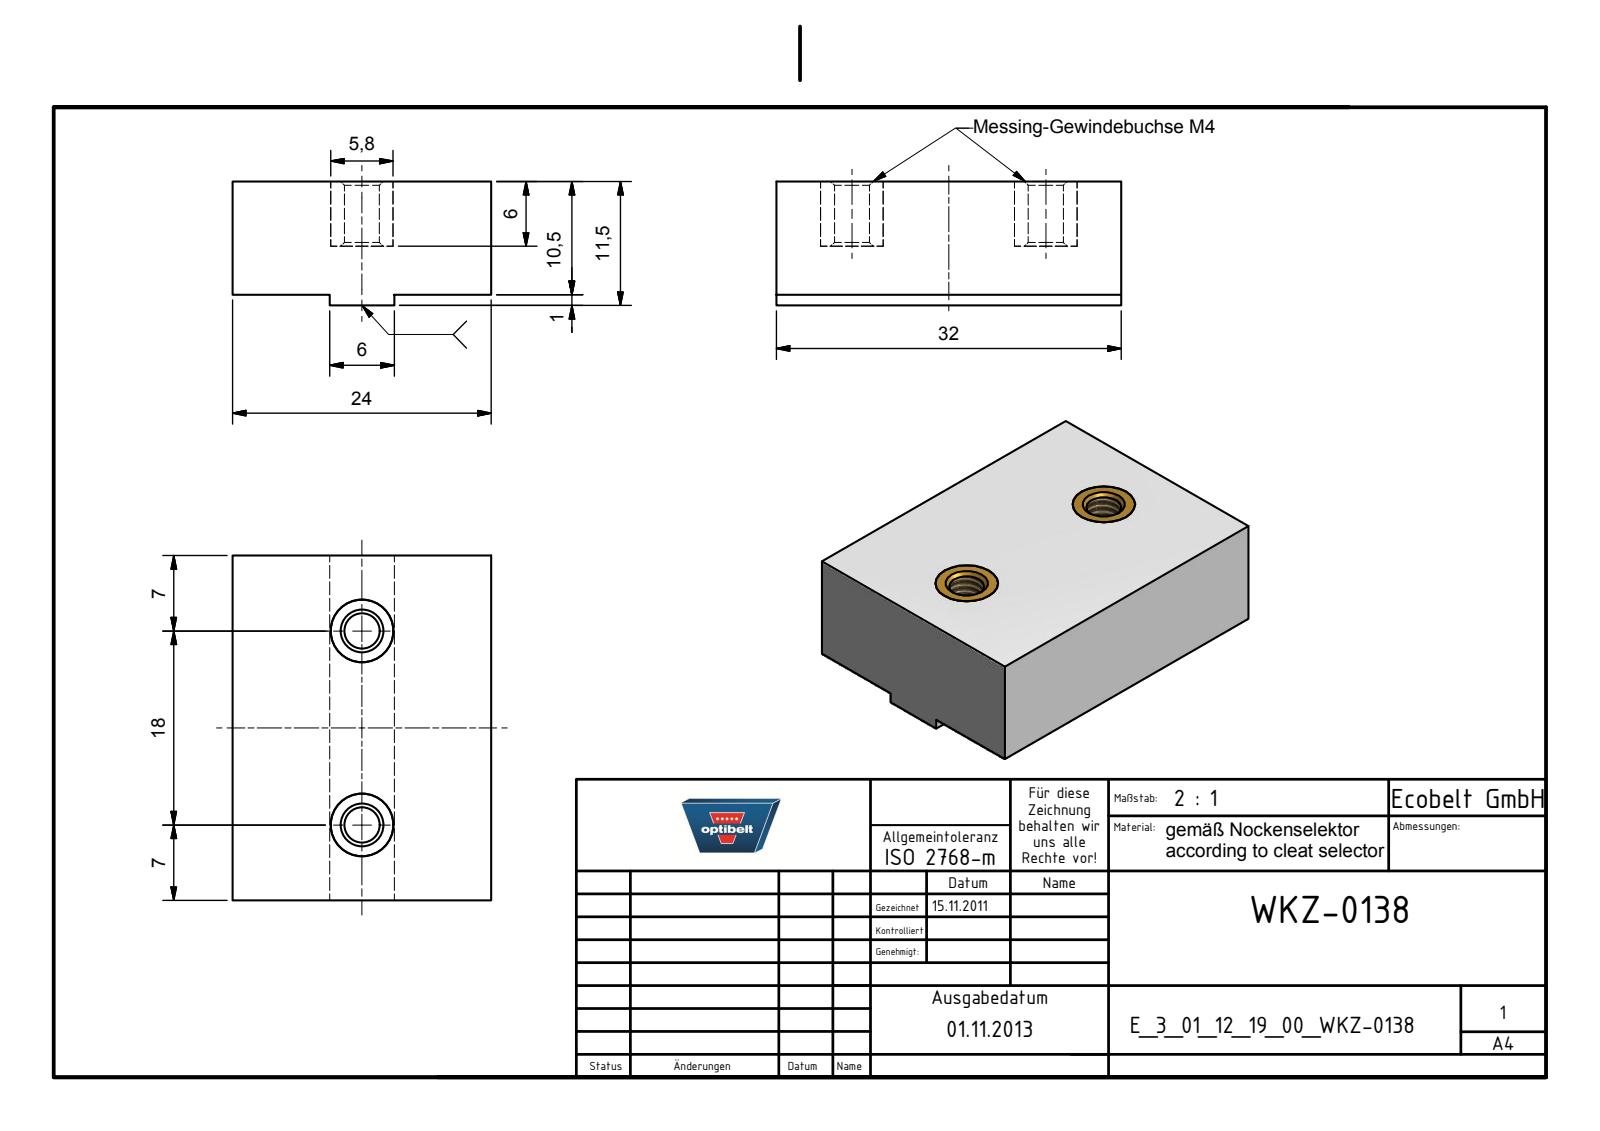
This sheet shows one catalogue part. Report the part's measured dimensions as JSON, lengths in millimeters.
{"part_name": "E_3_01_12_19_00_WKZ-0138; E_3_01_12_19_00_WKZ-0138-Teil1; E_3_01_12_19_00_WKZ-0138-Teil2", "step_written_by": "Autodesk Inventor 2025 (AUTOMOTIVE_DESIGN)", "units": "millimeters", "bodies": {"solids": 3, "faces": 26, "planar": 16, "cylindrical": 6, "other": 4}, "overall_size": [32, 24, 11.5], "volume_mm3": 8154, "surface_area_mm2": 3412, "round_holes": [[3.24, 2], [5.8, 2]], "face_to_face_distances": [10.5, 24, 32, 1, 11.5, 6, 5.5, 4.5, 9, 15], "hole_center_spacings": [18]}
